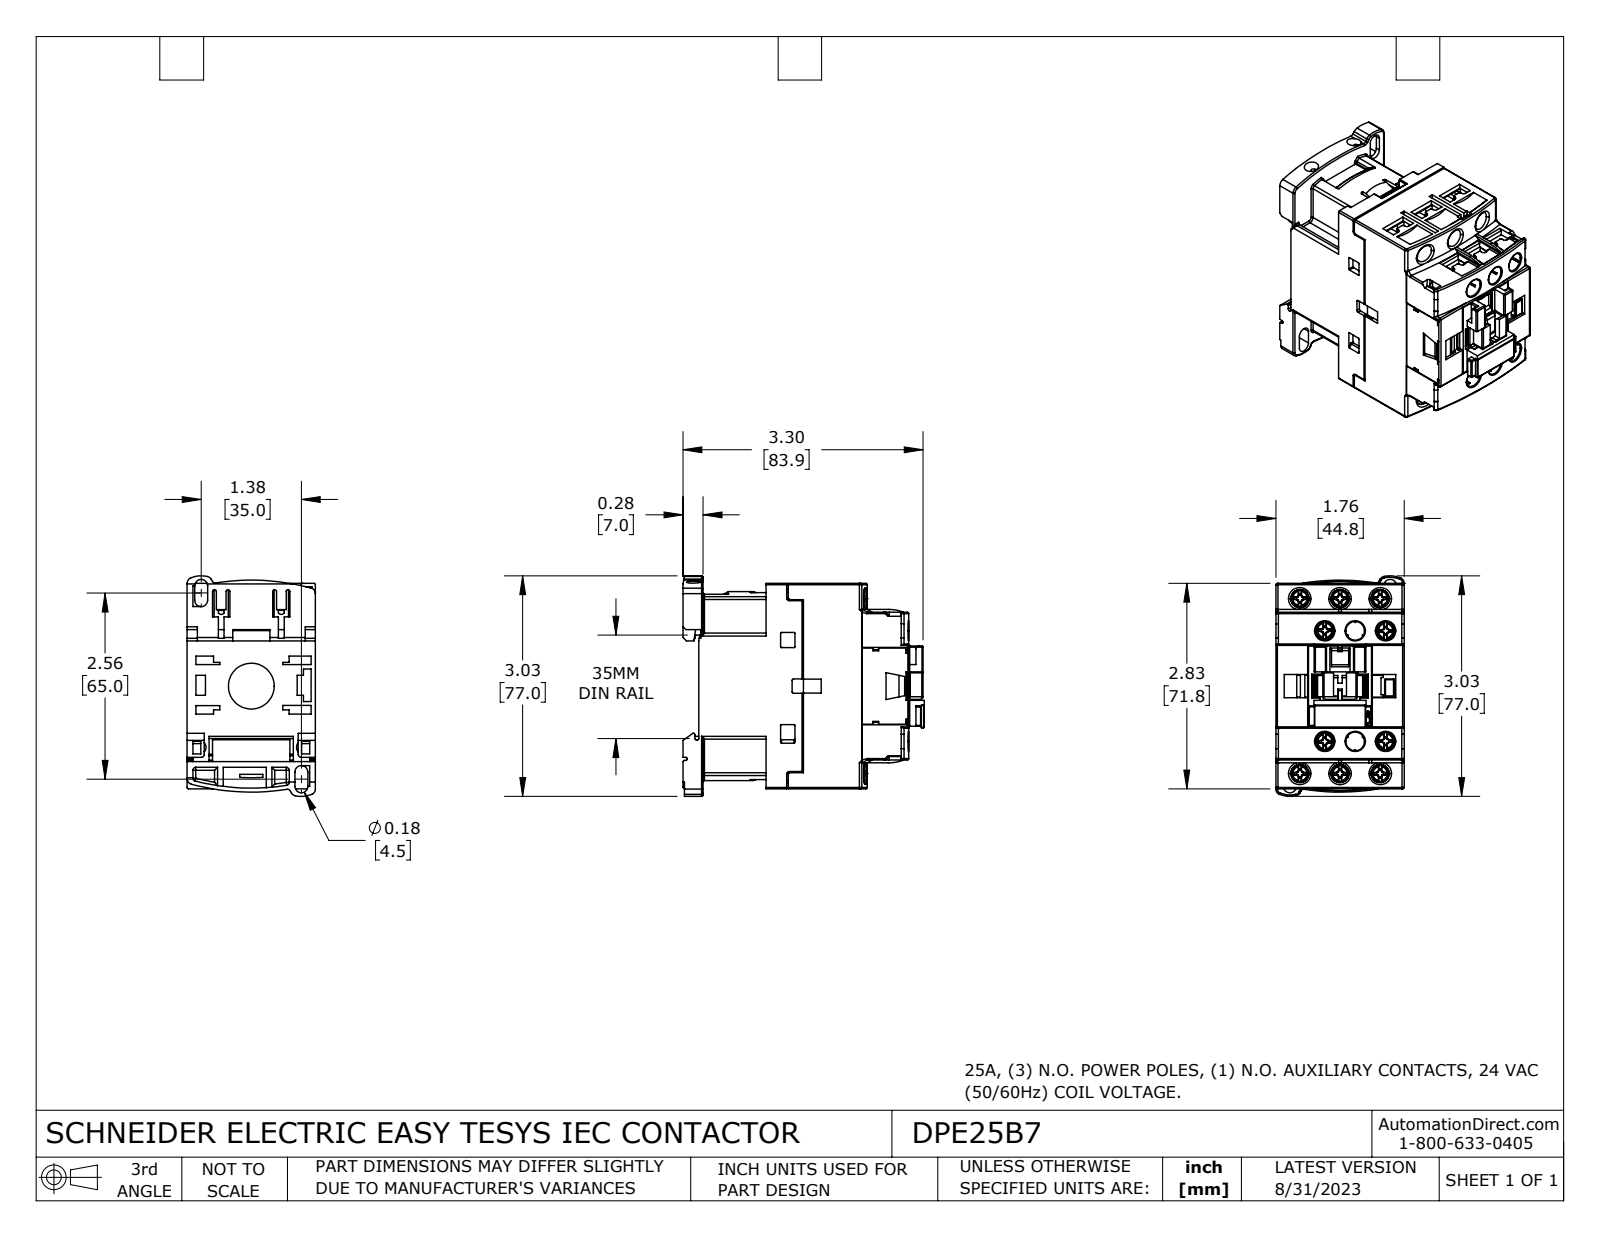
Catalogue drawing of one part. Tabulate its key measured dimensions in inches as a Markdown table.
| quantity | value |
| --- | --- |
| part name | DPE25B7 |
| STEP written by | SolidWorks 2021 (CONFIG_CONTROL_DESIGN) |
| units | inches |
| bodies | 20 solids, 3363 faces (2297 planar, 694 cylindrical, 372 other) |
| overall size | 3.317 × 3.031 × 1.783 |
| volume | 8.907 in³ |
| surface area | 103.4 in² |
| round holes (diameter × count) | 0.252 × 6, 0.256 × 6, 0.197 × 2, 0.167 × 1, 0.63 × 1 |
| round bosses / shafts (diameter × count) | 0.138 × 10, 0.108 × 10, 0.315 × 6 |
| partial cylindrical surfaces (radius × count) | 0.02 × 78, 0.012 × 64, 0.039 × 61, 0.006 × 42, 0.016 × 24, 0.63 × 9, 0.024 × 8, 0.079 × 7 |
| main face-to-face distances | 0.047, 1.764, 1.717, 0.321, 1.128, 0.807, 0.35, 2.78, 1.366, 1.118 |
| hole center spacings | 0.417, 0.488, 0.551, 0.558, 0.788, 0.878, 1.321, 1.576 |
